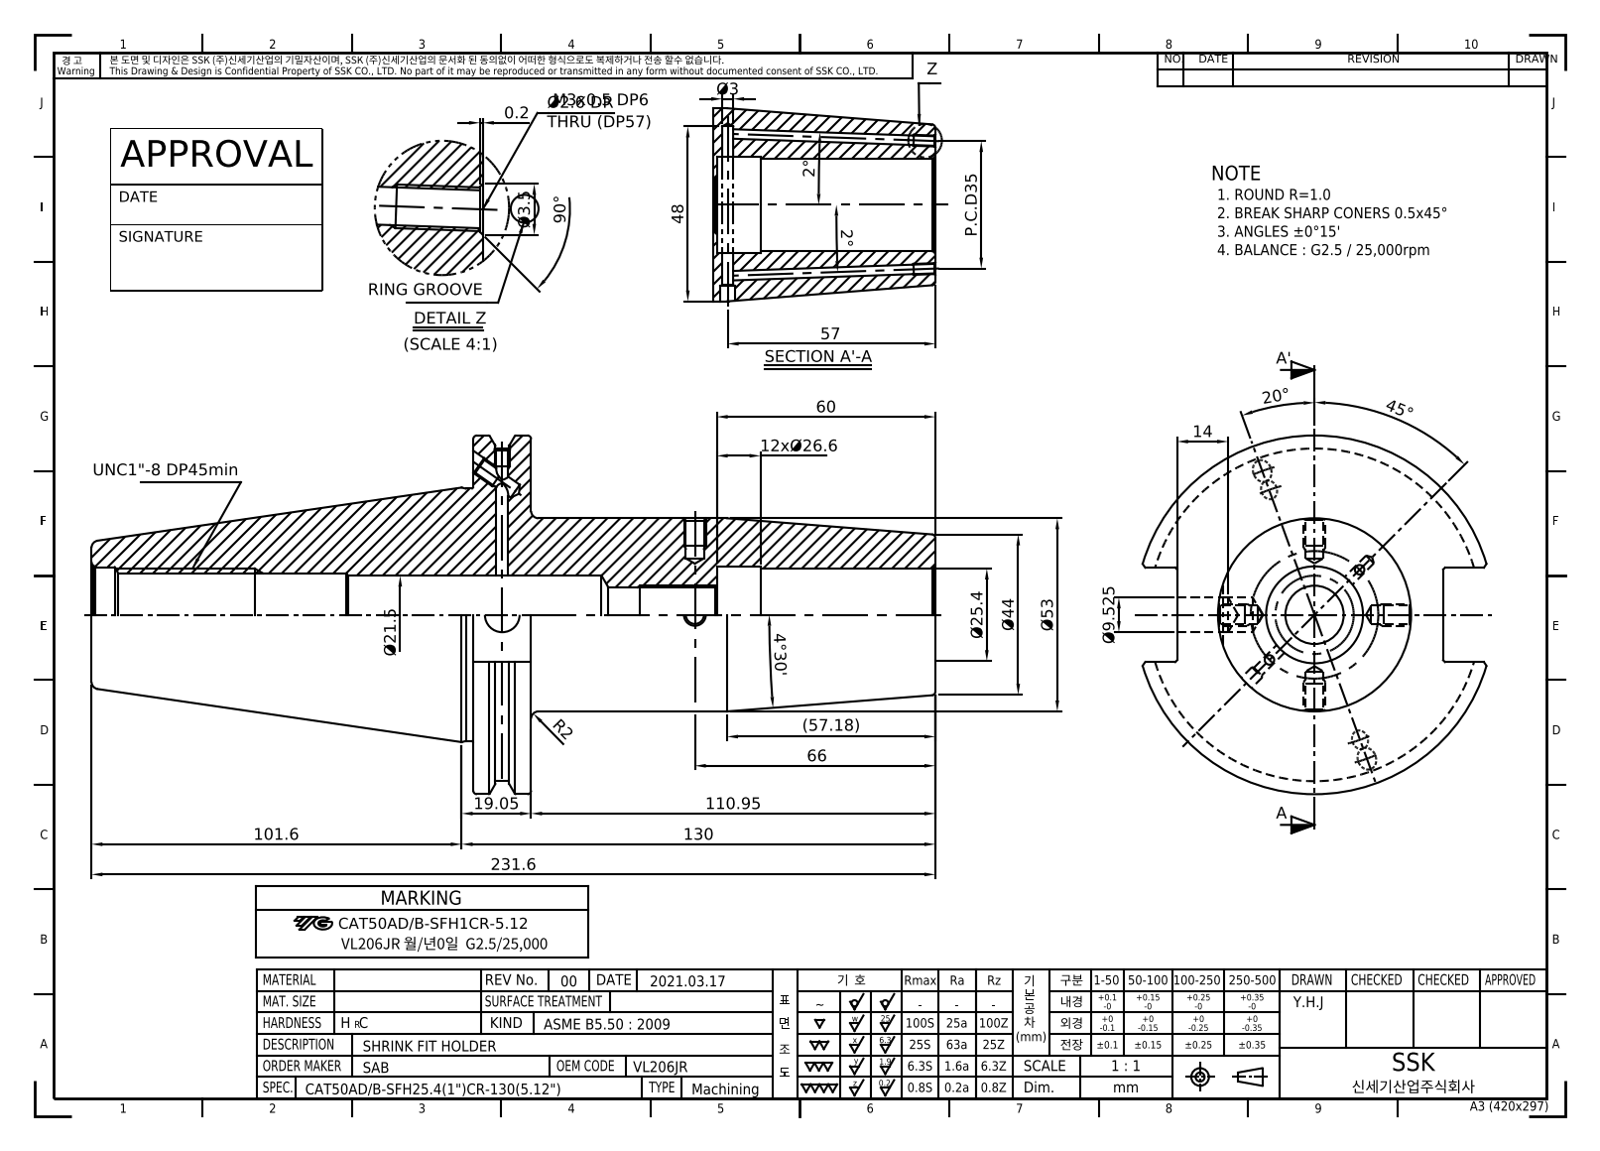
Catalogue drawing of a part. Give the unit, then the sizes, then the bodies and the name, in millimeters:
Units: millimetres
Overall size (bounding box): 231.6 × 98.42 × 94.69
Round holes (diameter × count): ⌀2.46 ×2, ⌀3.24 ×2, ⌀4.13 ×2, ⌀4.2 ×2, ⌀5 ×2, ⌀3 ×1, ⌀4 ×1, ⌀9.53 ×1, ⌀14.92 ×1, ⌀21.5 ×1, ⌀21.97 ×1, ⌀25.4 ×1
Round bosses / shafts (diameter × count): ⌀98.42 ×1, ⌀91.29 ×1, ⌀69.25 ×1, ⌀53 ×1
Main face-to-face distances: 15.88, 126.83, 110.95, 104.77, 120.65, 231.6, 171.6, 66.83, 50.95, 60
Volume: 498 923 mm³ · Surface area: 70 489 mm²
Bodies: 1 solid, 93 faces (37 planar, 32 cylindrical, 24 other)
Part name (STEP PRODUCT): LO-CAT50ADB-SFH25.4CR-130
STEP written by: Autodesk Inventor 2022 (AUTOMOTIVE_DESIGN)
